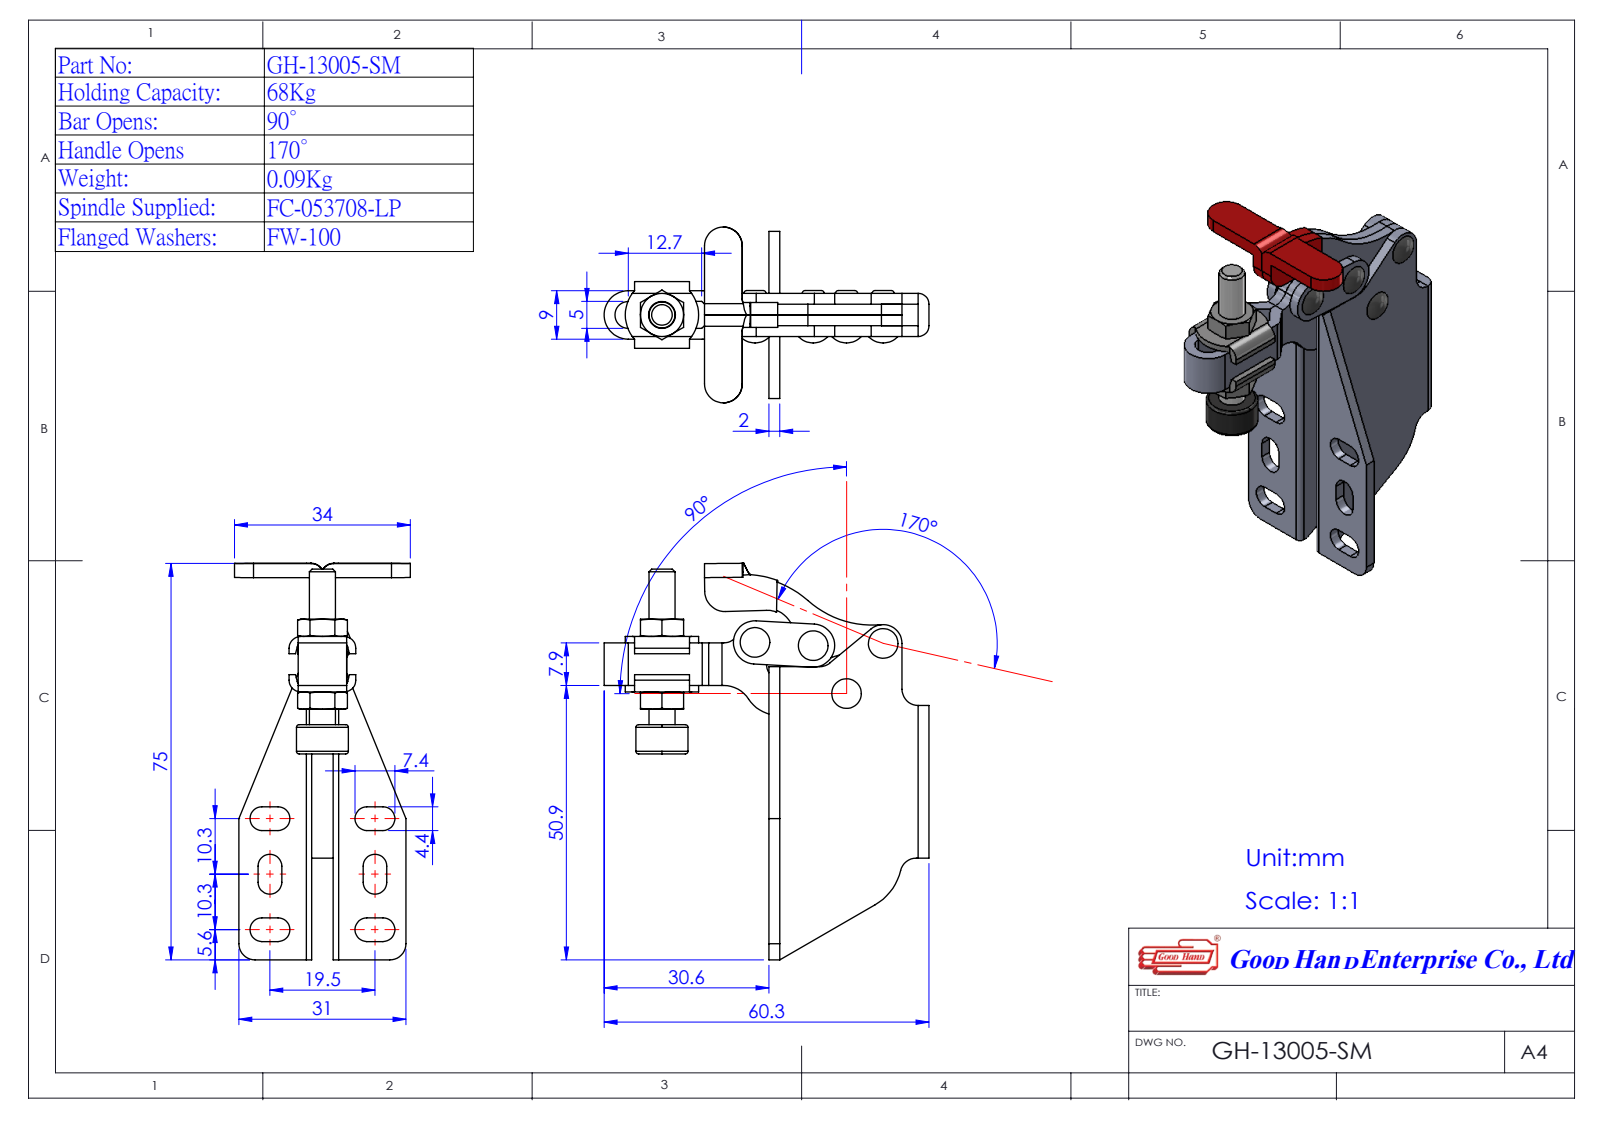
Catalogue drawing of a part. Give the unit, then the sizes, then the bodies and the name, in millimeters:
Units: millimetres
Overall size (bounding box): 73.89 × 60.3 × 33
Round holes (diameter × count): ⌀2.5 ×4
Round bosses / shafts (diameter × count): ⌀9.65 ×1, ⌀5 ×1
Partial cylindrical surfaces — rounded edges, fillets, slot ends (radius × count): R2.2 ×16, R1 ×10, R3 ×7, R3.5 ×4, R4 ×4, R1.01 ×2, R1.5 ×2, R1.7 ×2
Main face-to-face distances: 2, 6, 4, 8, 0.5, 0.49, 6.5, 4.5, 1.5, 2.31
Hole centre spacings: 10.83, 11.52, 13, 19.47, 23.8
Volume: 13 018 mm³ · Surface area: 15 427 mm²
Bodies: 6 solids, 302 faces (142 planar, 116 cylindrical, 44 other)
Part name (STEP PRODUCT): GH-13005-SM(簡化)-1; Group5^GH-13005-SM(簡化)-1; 11300501-2^GH-13005-SM(簡化)-1; 11300508-1^GH-13005-SM(簡化)-1 (+2 more)
STEP written by: SolidWorks 2016 (AUTOMOTIVE_DESIGN)
